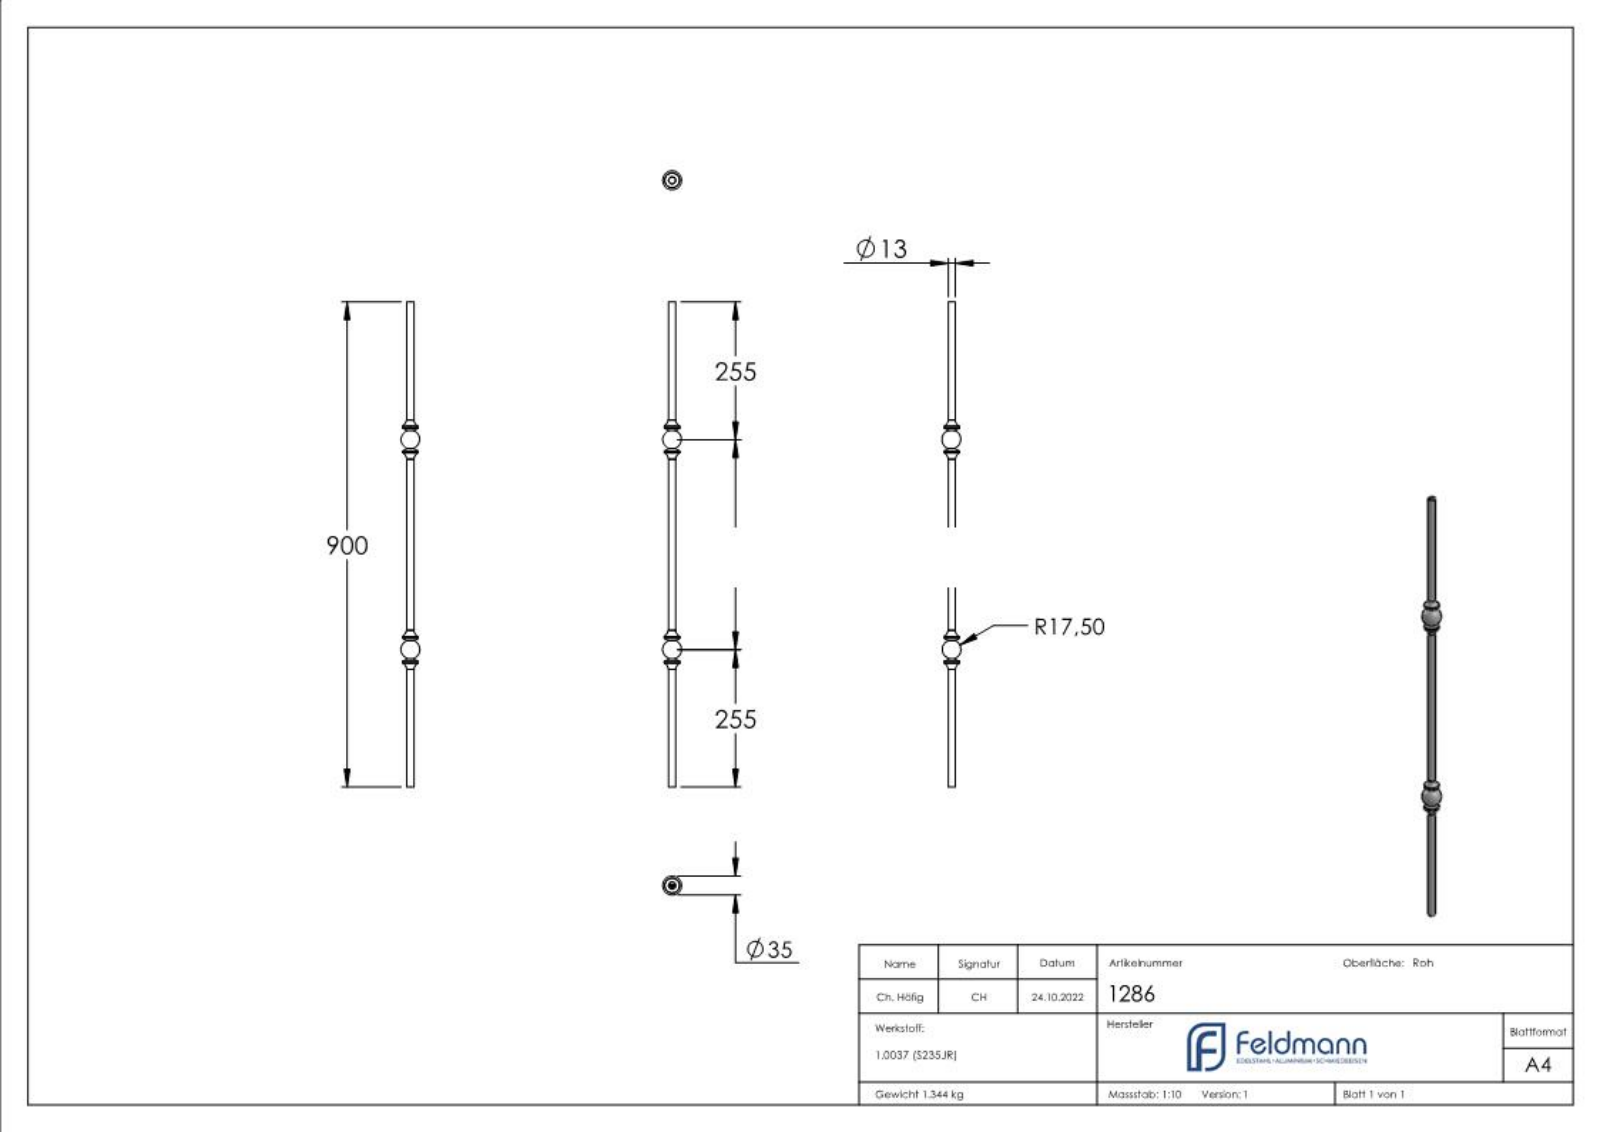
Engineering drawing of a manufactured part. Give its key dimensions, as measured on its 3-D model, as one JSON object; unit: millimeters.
{"part_name": "1286", "step_written_by": "SolidWorks 2018 (CONFIG_CONTROL_DESIGN)", "units": "millimeters", "bodies": {"solids": 1, "faces": 198, "planar": 89, "cylindrical": 7, "other": 102}, "overall_size": [900, 35, 35], "volume_mm3": 172322, "surface_area_mm2": 45216, "round_bosses_or_shafts": [[28, 1], [13, 1]], "face_to_face_distances": [900, 899.9, 3.66, 0.57, 2.7, 0.39, 2.97, 0.69, 1.12, 4.09]}
